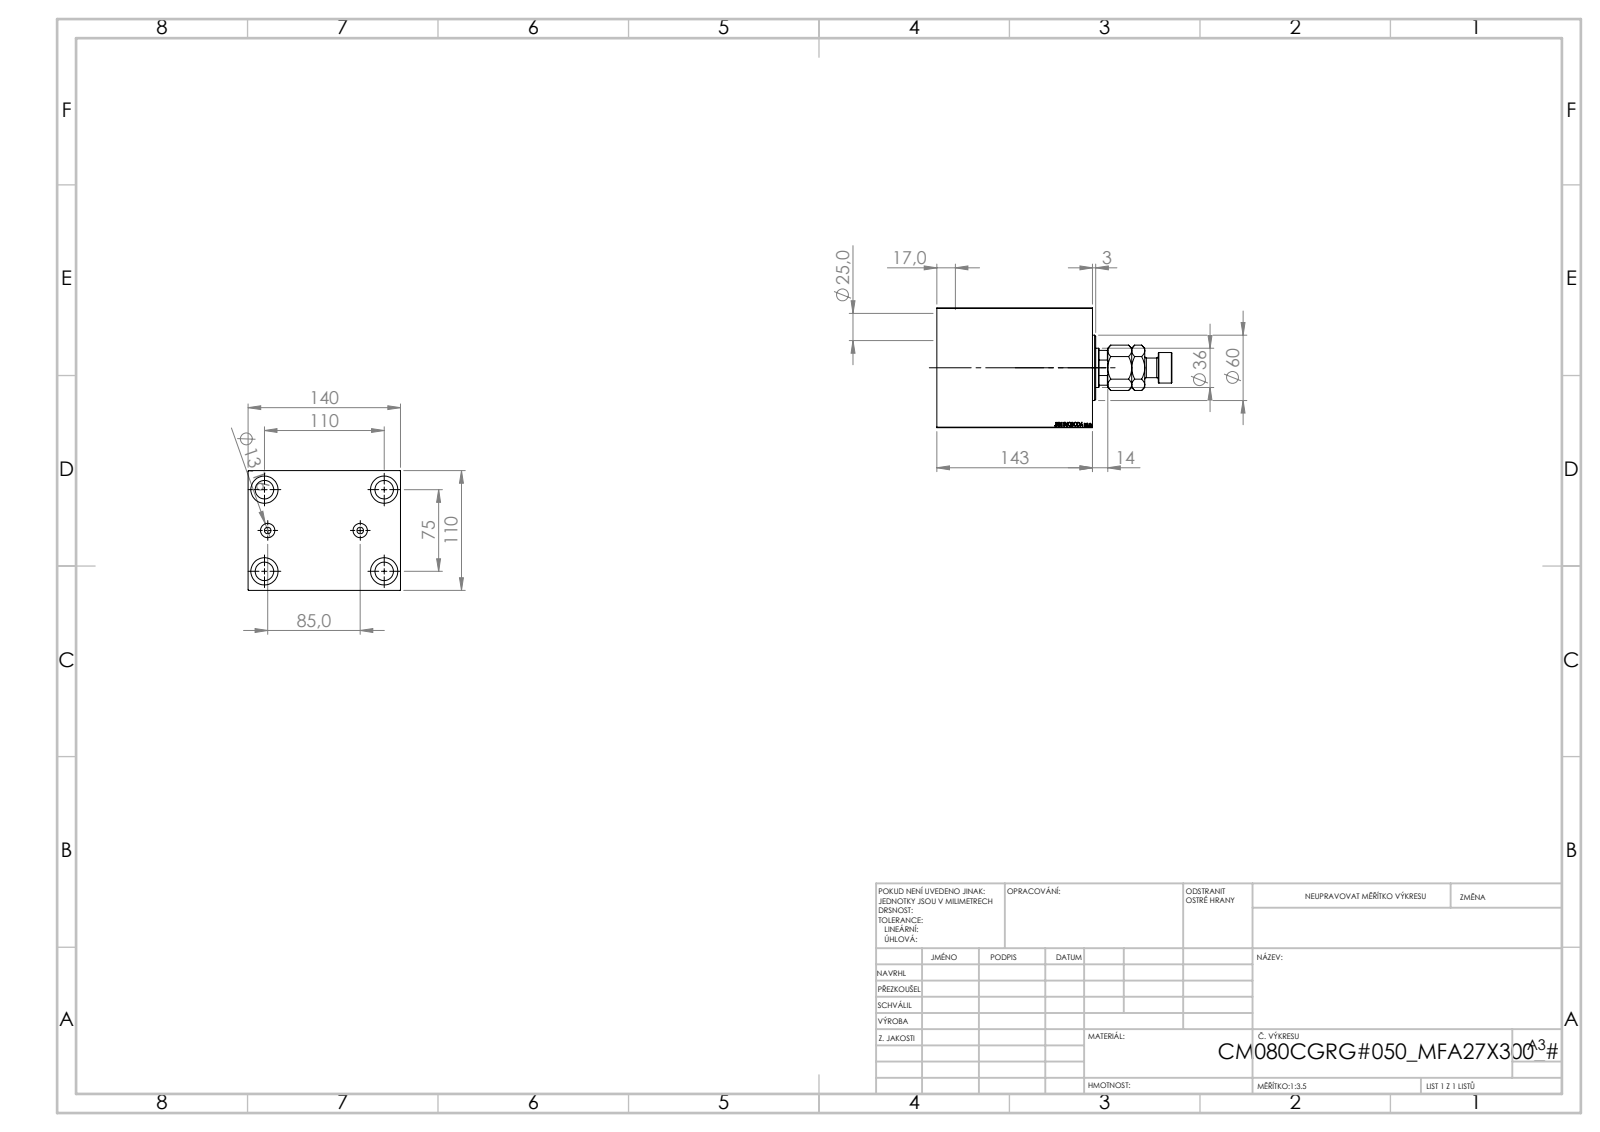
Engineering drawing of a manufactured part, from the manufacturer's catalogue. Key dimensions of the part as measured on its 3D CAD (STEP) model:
Part name (STEP PRODUCT): V450CM_C_VCP; MFA; V450CM_VC_B; V450CM_C_Body
STEP written by: SolidWorks 2019 (CONFIG_CONTROL_DESIGN)
Units: millimetres
Bodies: 4 solids, 915 faces (427 planar, 62 cylindrical, 426 other)
Overall size (bounding box): 216 × 140 × 110
Volume: 1 876 000 mm³ · Surface area: 212 342 mm²
Round holes (diameter × count): ⌀17 ×4, ⌀25 ×4, ⌀6 ×2, ⌀13.16 ×2, ⌀25.5 ×1, ⌀36 ×1, ⌀39.5 ×1, ⌀80 ×1, ⌀82 ×1, ⌀87 ×1
Round bosses / shafts (diameter × count): ⌀60 ×1, ⌀28 ×1, ⌀18 ×1
Partial cylindrical surfaces — rounded edges, fillets, slot ends (radius × count): R17.5 ×1
Main face-to-face distances: 110, 140, 143, 88.25, 54.75, 133, 10, 83, 78.25, 60
Hole centre spacings: 39.53, 66.57, 104.46, 42.5, 75, 110, 133.14, 85
